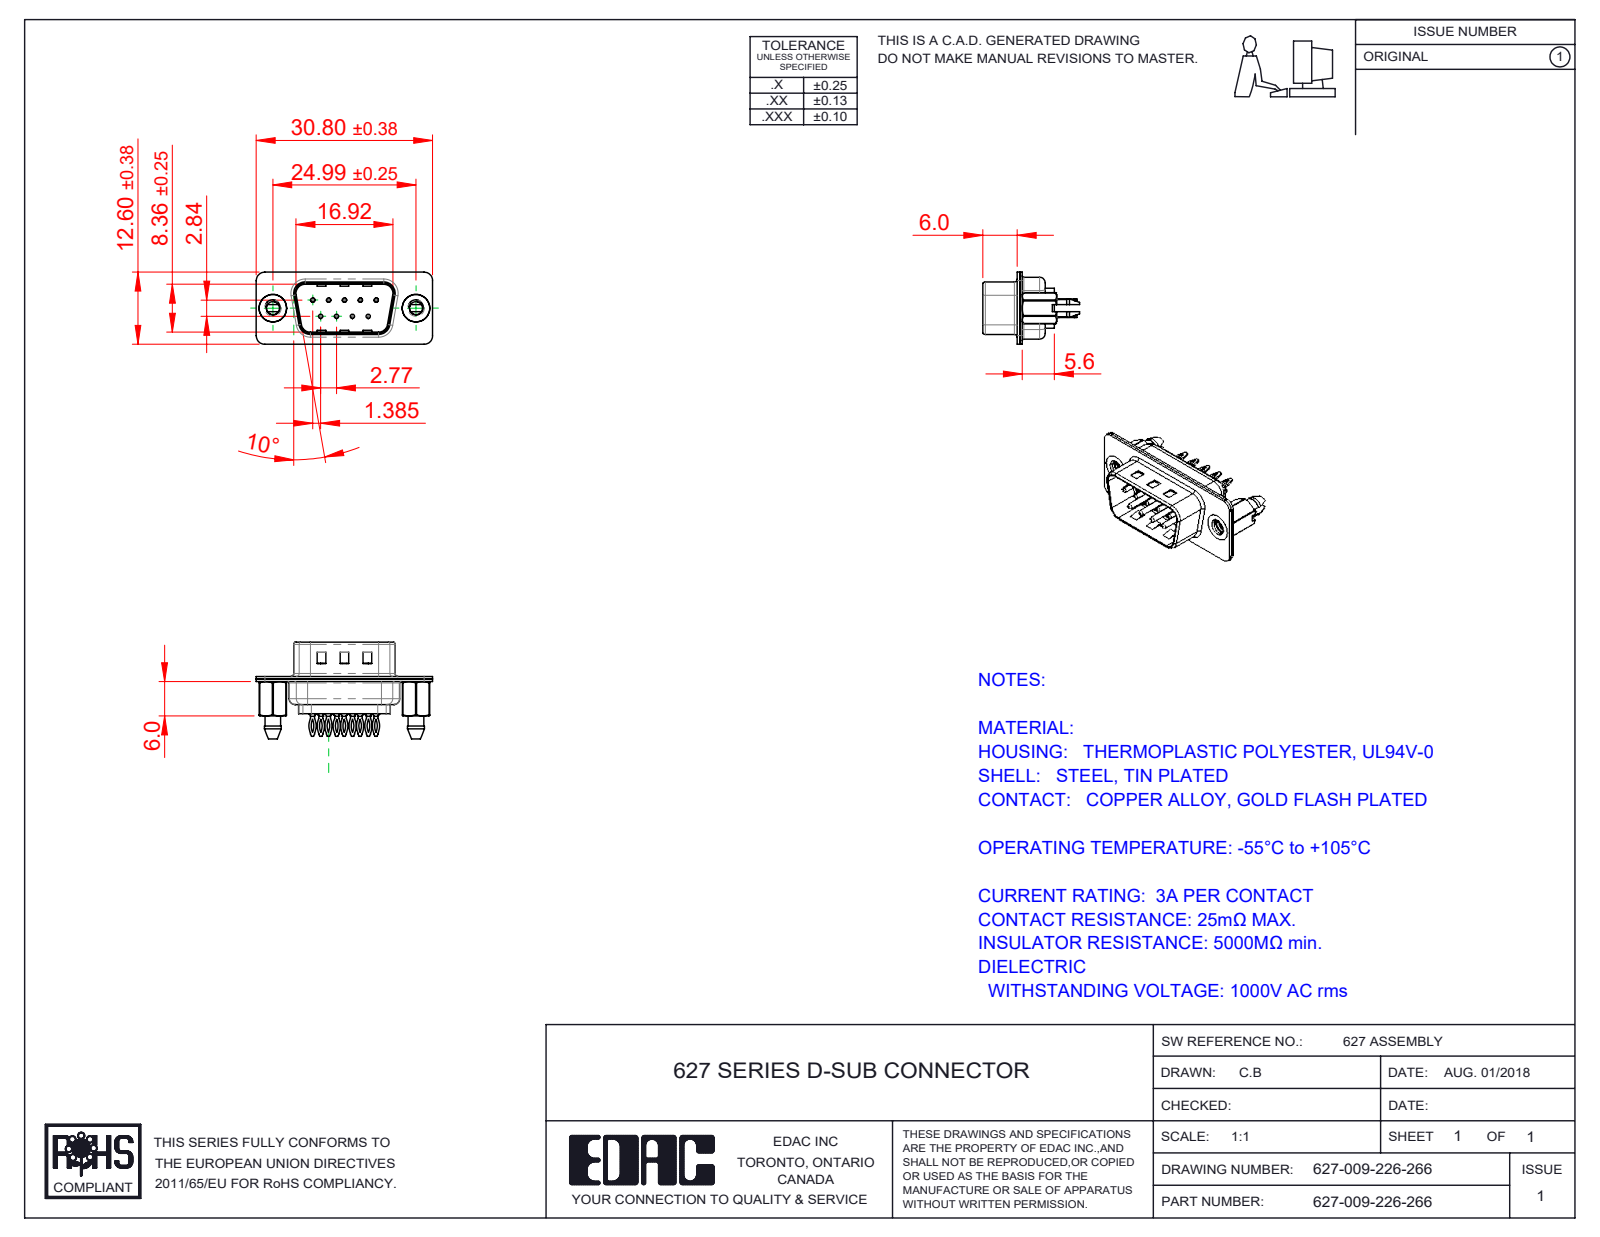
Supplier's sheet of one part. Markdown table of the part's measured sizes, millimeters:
| quantity | value |
| --- | --- |
| part name | 627 Shell Rear_09 Contacts; 627 Housing_09 LP; 627 4-40 Threaded Boardlock_LP; 627 Contact Row 1_26L (+3 more) |
| STEP written by | SolidWorks 2020 (CONFIG_CONTROL_DESIGN) |
| units | millimeters |
| bodies | 14 solids, 1062 faces (319 planar, 440 cylindrical, 303 other) |
| overall size | 30.8 × 16.9 × 12.6 |
| volume | 1 427 mm³ |
| surface area | 4 197 mm² |
| round holes (diameter × count) | 0.35 × 9, 1.1 × 9, 1.6 × 9, 2.26 × 2, 4 × 2, 4.8 × 2 |
| round bosses / shafts (diameter × count) | 2 × 9, 1.5 × 9, 0.75 × 9, 4.9 × 2 |
| partial cylindrical surfaces (radius × count) | 1.5 × 20, 2.92 × 18, 3.33 × 18, 2 × 12, 1.6 × 10, 0.5 × 8, 0.25 × 4, 0.6 × 4 |
| main face-to-face distances | 0.4, 0.45, 0.9, 0.82, 9.58, 1.4, 8.76, 6.5, 0.5, 1.5 |
| hole center spacings | 3.16, 2.77, 5.54, 5.03, 5.04, 8.31, 7.48, 7.49 |
